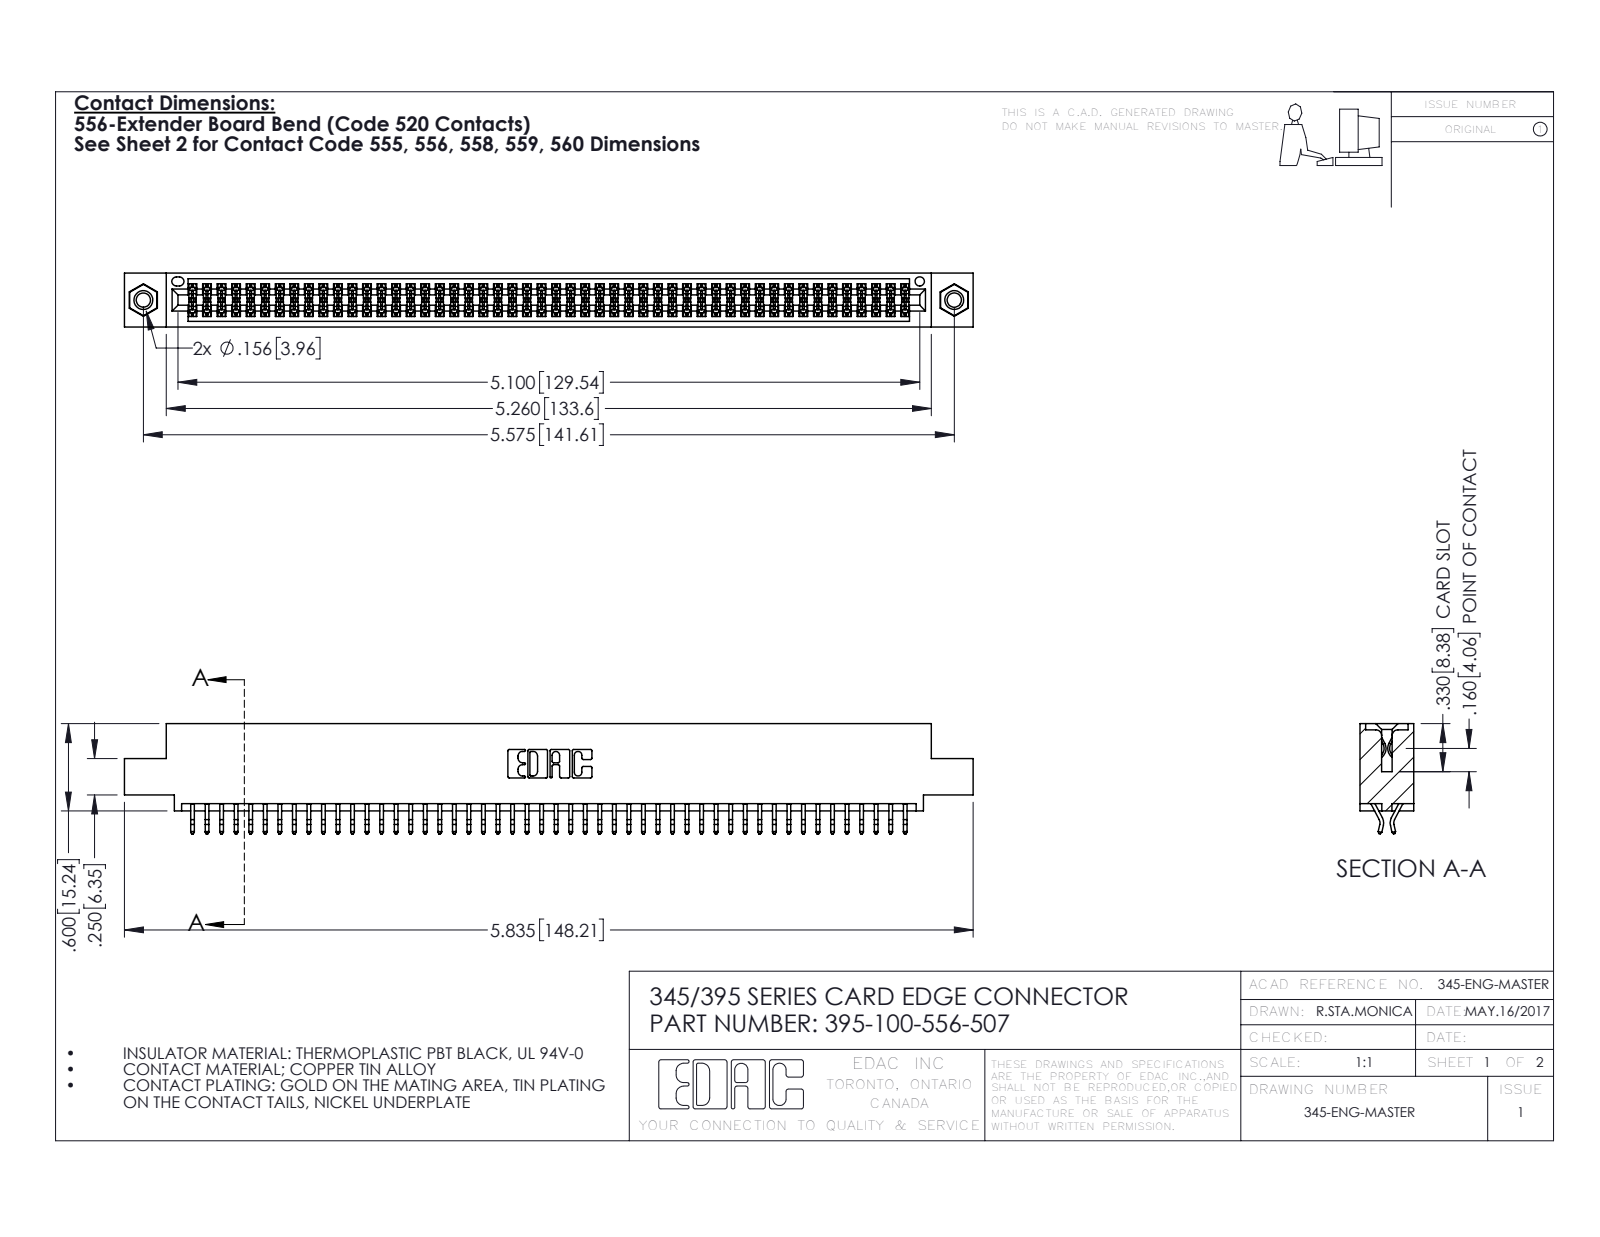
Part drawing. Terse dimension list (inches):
name: 345 Part_0.110 Offset - 0.156 Dia-TI; 345-250-001_345-250-005-103; 395-100-556-507; 345-292-001_556 Tail
written by: SolidWorks 2016 (CONFIG_CONTROL_DESIGN)
unit: in
bodies: 103 solids, 5790 faces (3816 planar, 1958 cylindrical, 16 other)
size: 5.835 × 0.757 × 0.37
volume: 0.878 in³; area: 33.24 in²
holes: 2× ⌀0.098, 2× ⌀0.125, 2× ⌀0.156, 1× ⌀0.064
bosses: 2× ⌀0.155
rounds: 150× R0.006, 22× R0.01, 6× R0.007, 6× R0.031, 3× R0.026, 2× R0.01, 2× R0.014, 2× R0.019
face distances: 0.072, 0.298, 0.37, 0.2, 0.025, 0.098, 0.272, 0.225, 0.175, 0.149
hole spacings: 0.27, 5.339, 5.575
